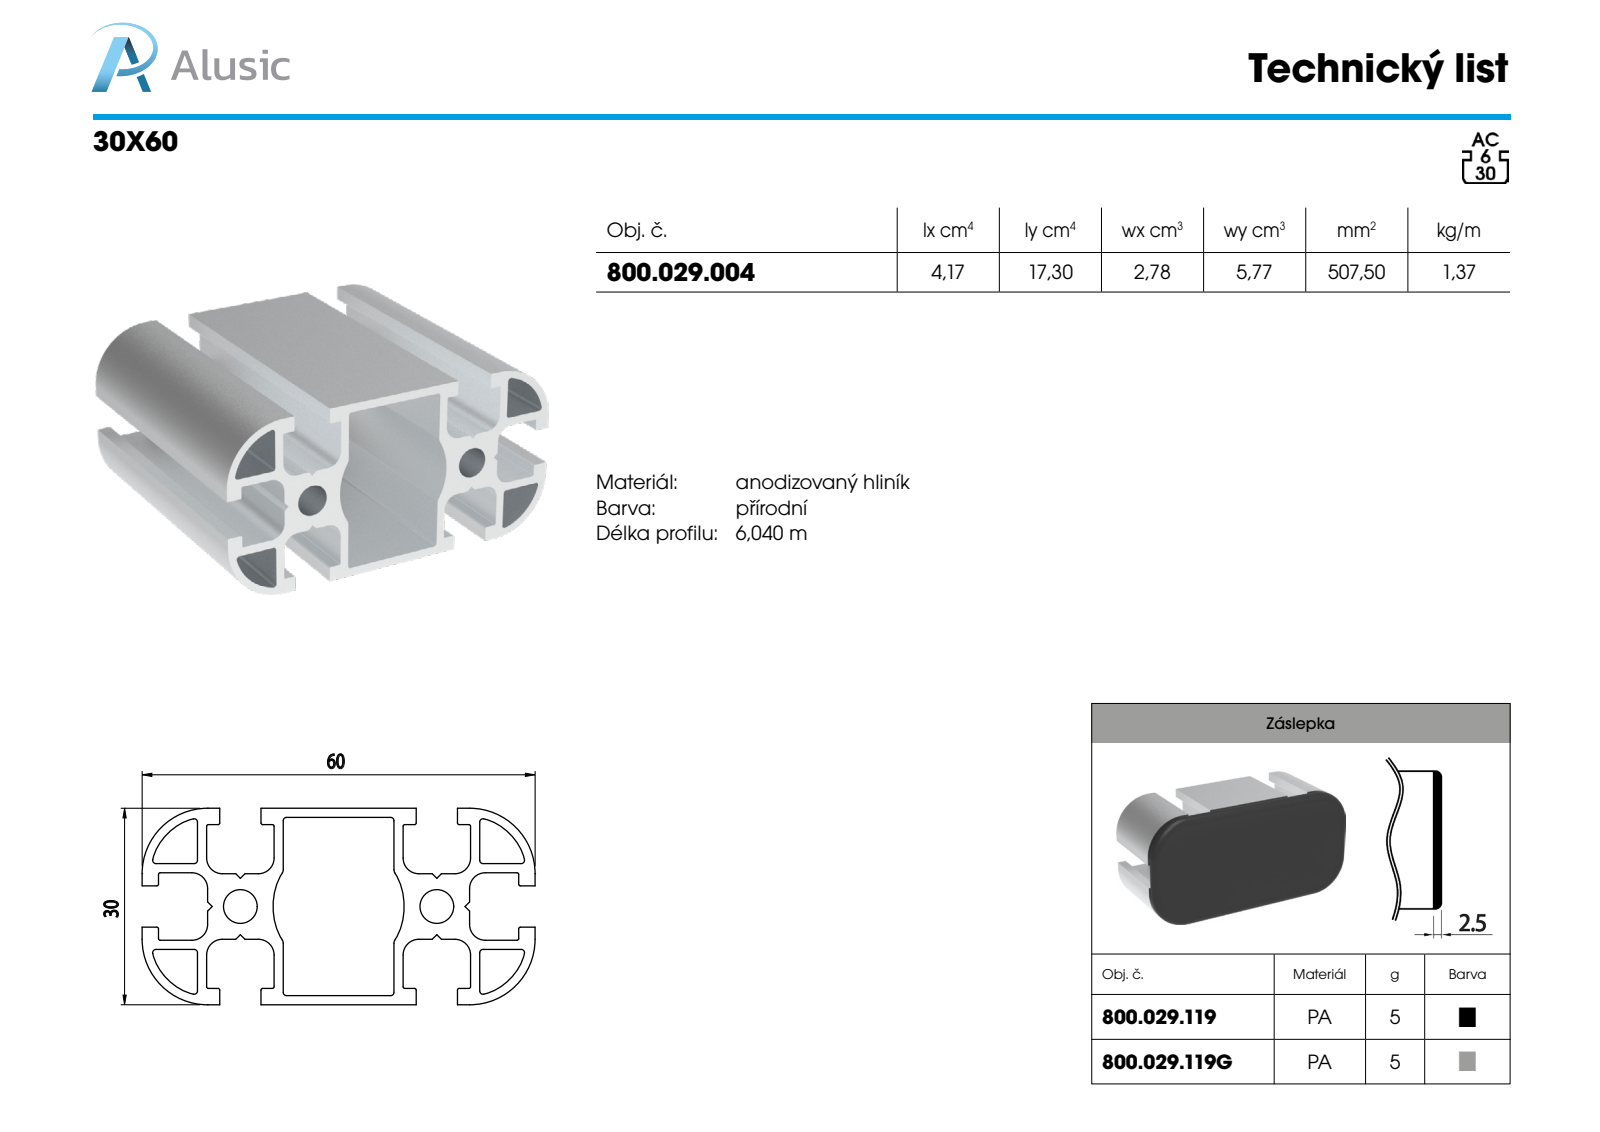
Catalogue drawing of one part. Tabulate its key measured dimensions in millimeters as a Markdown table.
| quantity | value |
| --- | --- |
| part name | 800.029.119 |
| STEP written by | SolidWorks 2012 (CONFIG_CONTROL_DESIGN) |
| units | millimeters |
| bodies | 1 solid, 88 faces (32 planar, 34 cylindrical, 22 other) |
| overall size | 60 × 30 × 8.5 |
| volume | 4 467 mm³ |
| surface area | 4 473 mm² |
| round holes (diameter × count) | 3.5 × 4 |
| round bosses / shafts (diameter × count) | 5 × 4 |
| partial cylindrical surfaces (radius × count) | 2 × 4, 10 × 4, 2.58 × 2 |
| main face-to-face distances | 2.5, 1.2, 30, 14.4, 15.6, 4, 6.5, 28.8, 31.2, 2 |
| hole center spacings | 18.68, 48.68, 52.14 |
